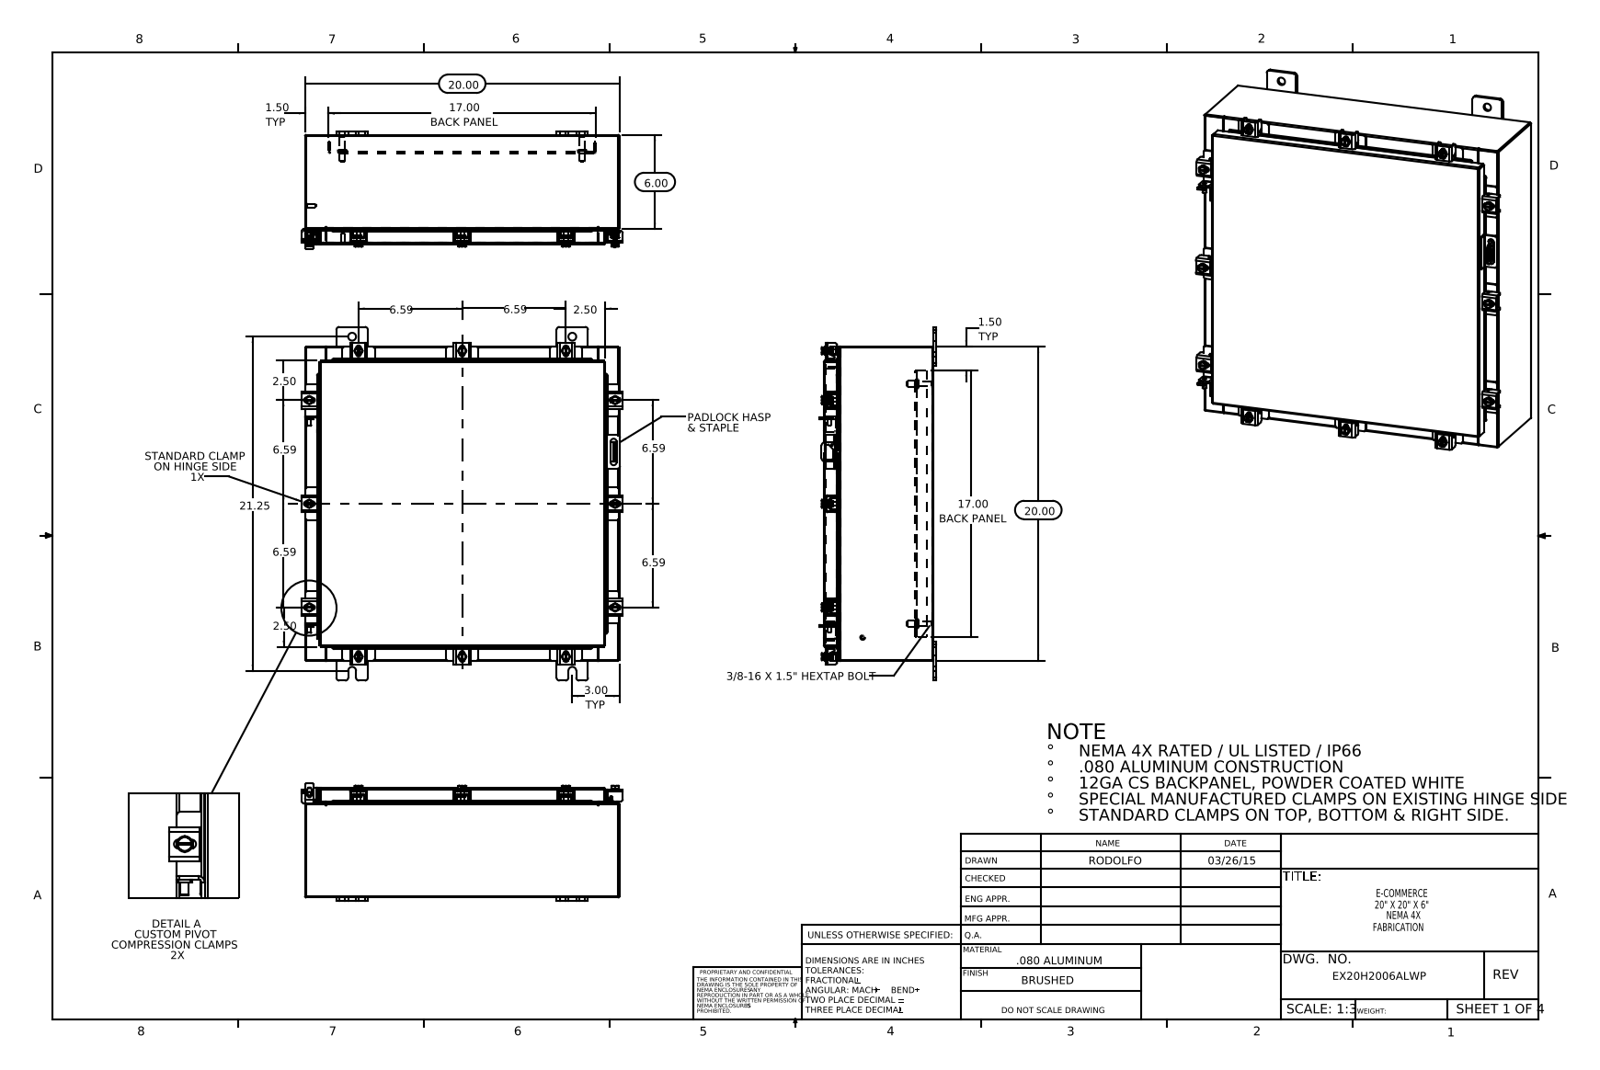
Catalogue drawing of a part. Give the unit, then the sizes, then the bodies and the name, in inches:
Units: inches
Overall size (bounding box): 22.5 × 20.421 × 7.453
Round holes (diameter × count): ⌀0.213 ×12, ⌀0.26 ×12, ⌀0.5 ×8, ⌀0.125 ×1, ⌀0.25 ×1
Round bosses / shafts (diameter × count): ⌀0.5 ×12, ⌀0.25 ×12, ⌀0.399 ×10, ⌀0.625 ×4, ⌀0.375 ×4, ⌀0.33 ×4, ⌀0.315 ×2, ⌀0.236 ×2
Partial cylindrical surfaces — rounded edges, fillets, slot ends (radius × count): R0.06 ×54, R0.013 ×24, R0.141 ×24, R0.19 ×24, R0.088 ×22, R0.12 ×22, R0.09 ×18, R0.05 ×17
Main face-to-face distances: 0.075, 6.9, 19.925, 6.975, 6.826, 0.104, 1, 1.075, 5.826, 5.9
Hole centre spacings: 6.594, 10.217, 16.617, 18.998, 20.539, 2.34, 14.374, 17.381
Volume: 149.7 in³ · Surface area: 3 735 in²
Bodies: 81 solids, 2018 faces (1075 planar, 783 cylindrical, 160 other)
Part name (STEP PRODUCT): EX20H2006ALWP Clamp Assembly; EX20H2006ALWP Padlock Hasp; HW-CLN-NH-20330; Special Clamp Assembly (+8 more)
STEP written by: SolidWorks 2014 (CONFIG_CONTROL_DESIGN)
